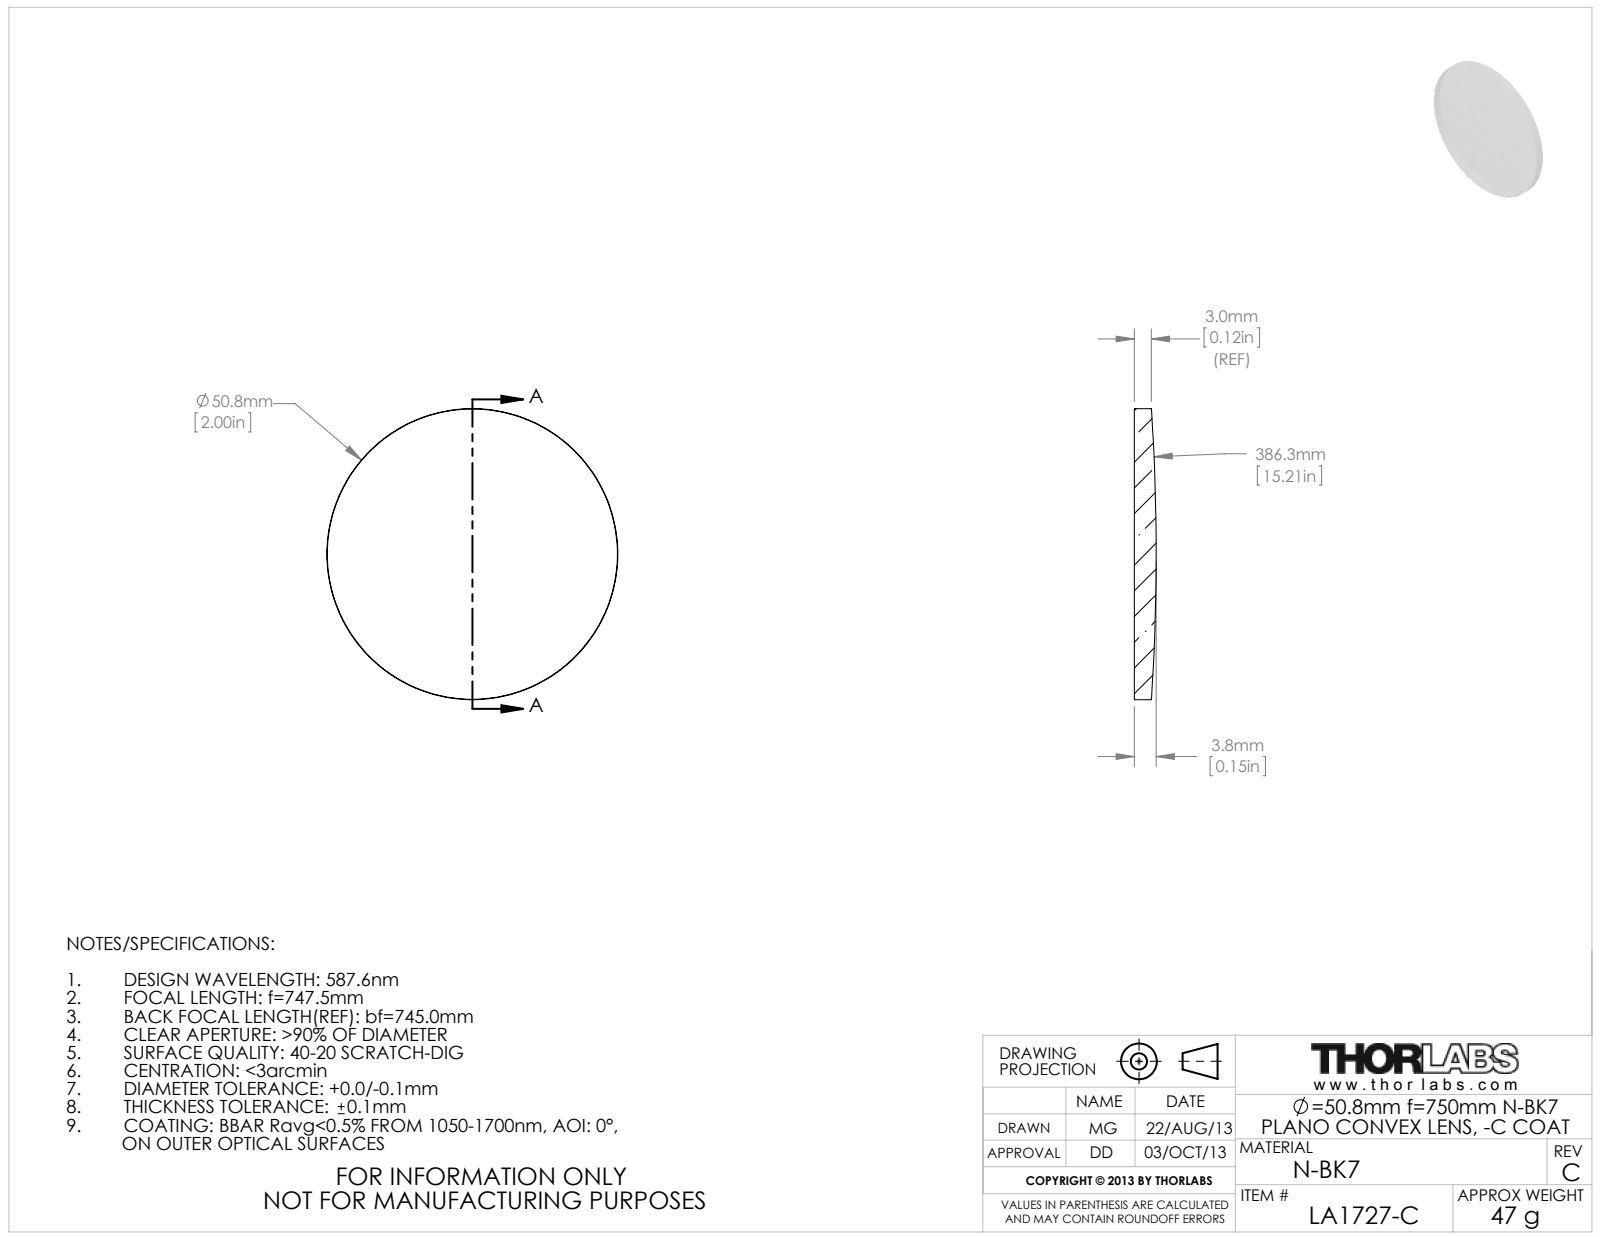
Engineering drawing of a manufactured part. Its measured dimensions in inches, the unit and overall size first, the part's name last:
Units: inches
Overall size (bounding box): 2 × 2 × 0.151
Round bosses / shafts (diameter × count): ⌀2 ×1
Bodies: 0 solids, 5 faces (1 planar, 2 cylindrical, 2 other)
Part name (STEP PRODUCT): 4611-E0W
STEP written by: SolidWorks 2009 (AUTOMOTIVE_DESIGN)
